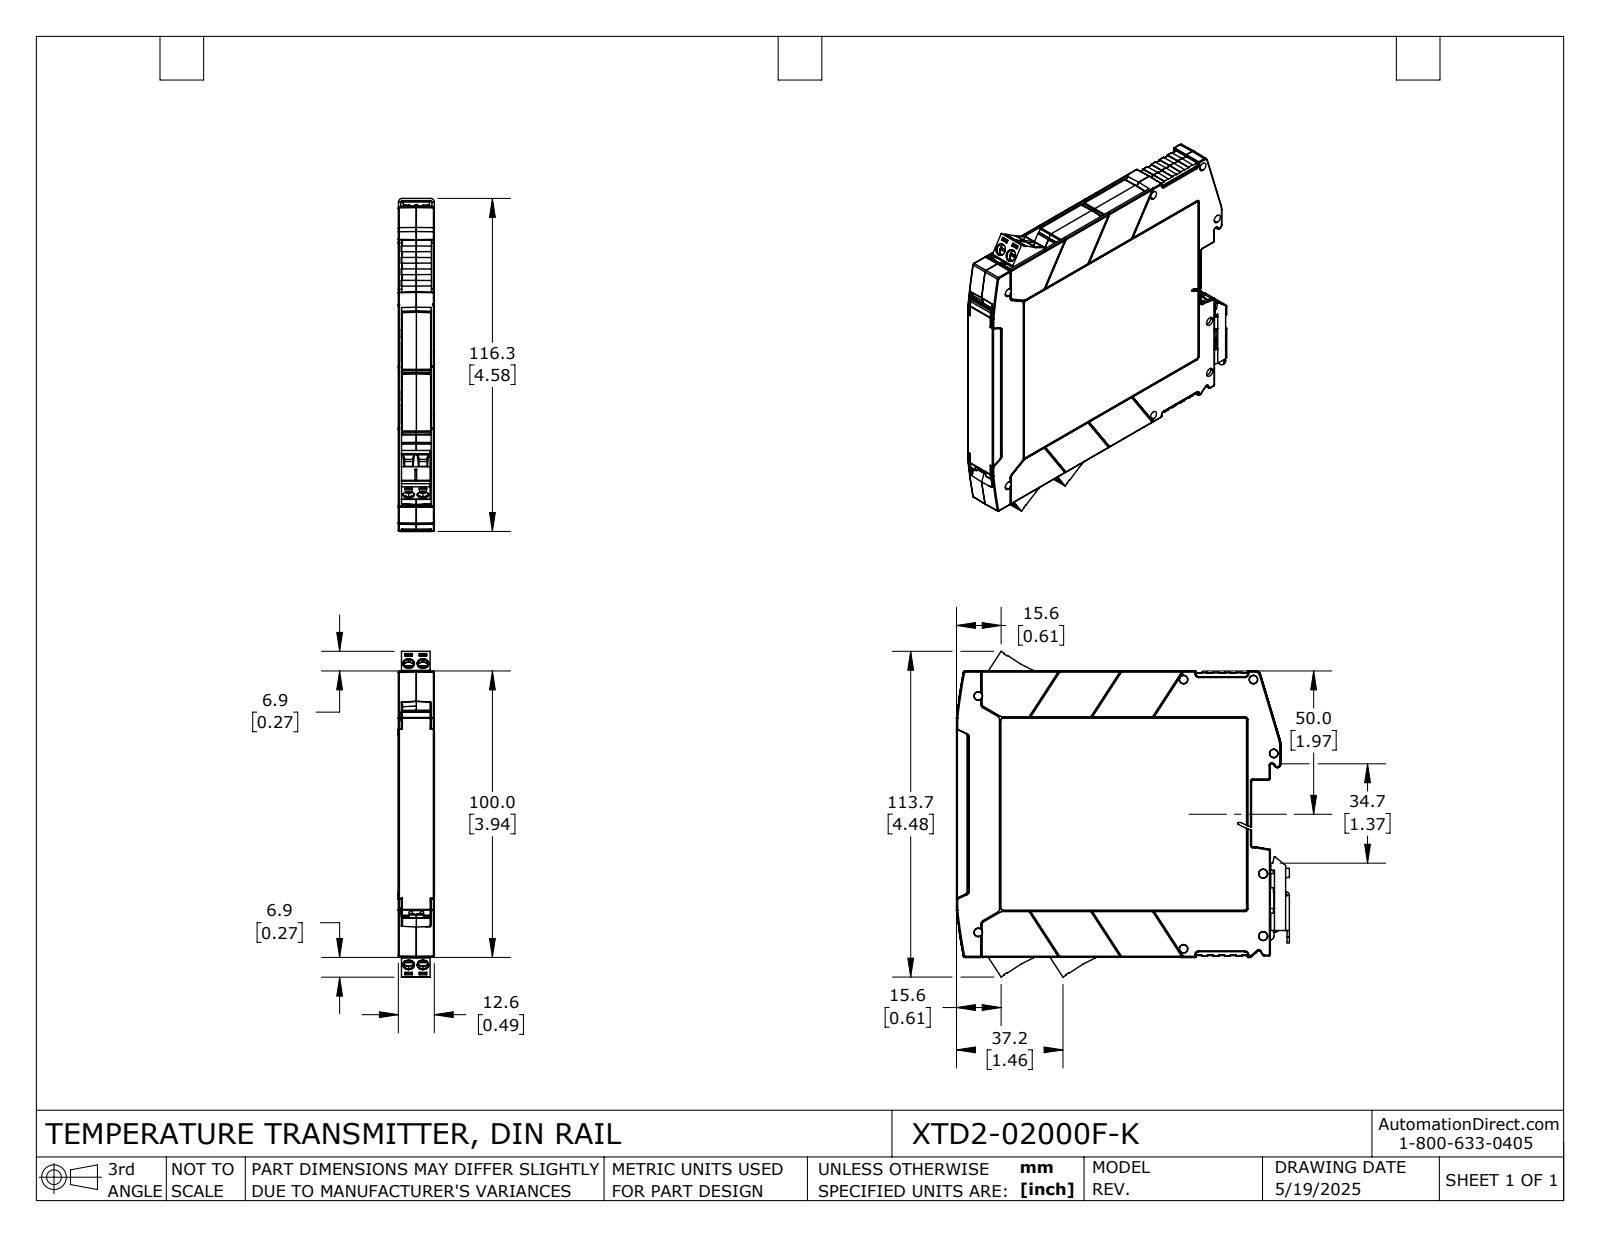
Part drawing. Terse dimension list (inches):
name: XTD2-02000F-K
written by: SolidWorks 2024 (AUTOMOTIVE_DESIGN)
unit: in
bodies: 14 solids, 3337 faces (1910 planar, 596 cylindrical, 831 other)
size: 4.577 × 4.478 × 0.496
volume: 2.41 in³; area: 101.5 in²
holes: 6× ⌀0.063, 6× ⌀0.11, 6× ⌀0.152, 6× ⌀0.159
bosses: 6× ⌀0.156, 6× ⌀0.098, 2× ⌀0.059, 2× ⌀0.053
rounds: 89× R0.008, 78× R0.012, 71× R0.02, 22× R0.039, 20× R0.004, 13× R0.016, 12× R0.006, 8× R0.028
face distances: 0.049, 0.445, 0.494, 0.396, 0.043, 0.451, 0.402, 0.031, 0.198, 0.247
hole spacings: 0.197, 0.464, 0.504, 0.713, 0.739
